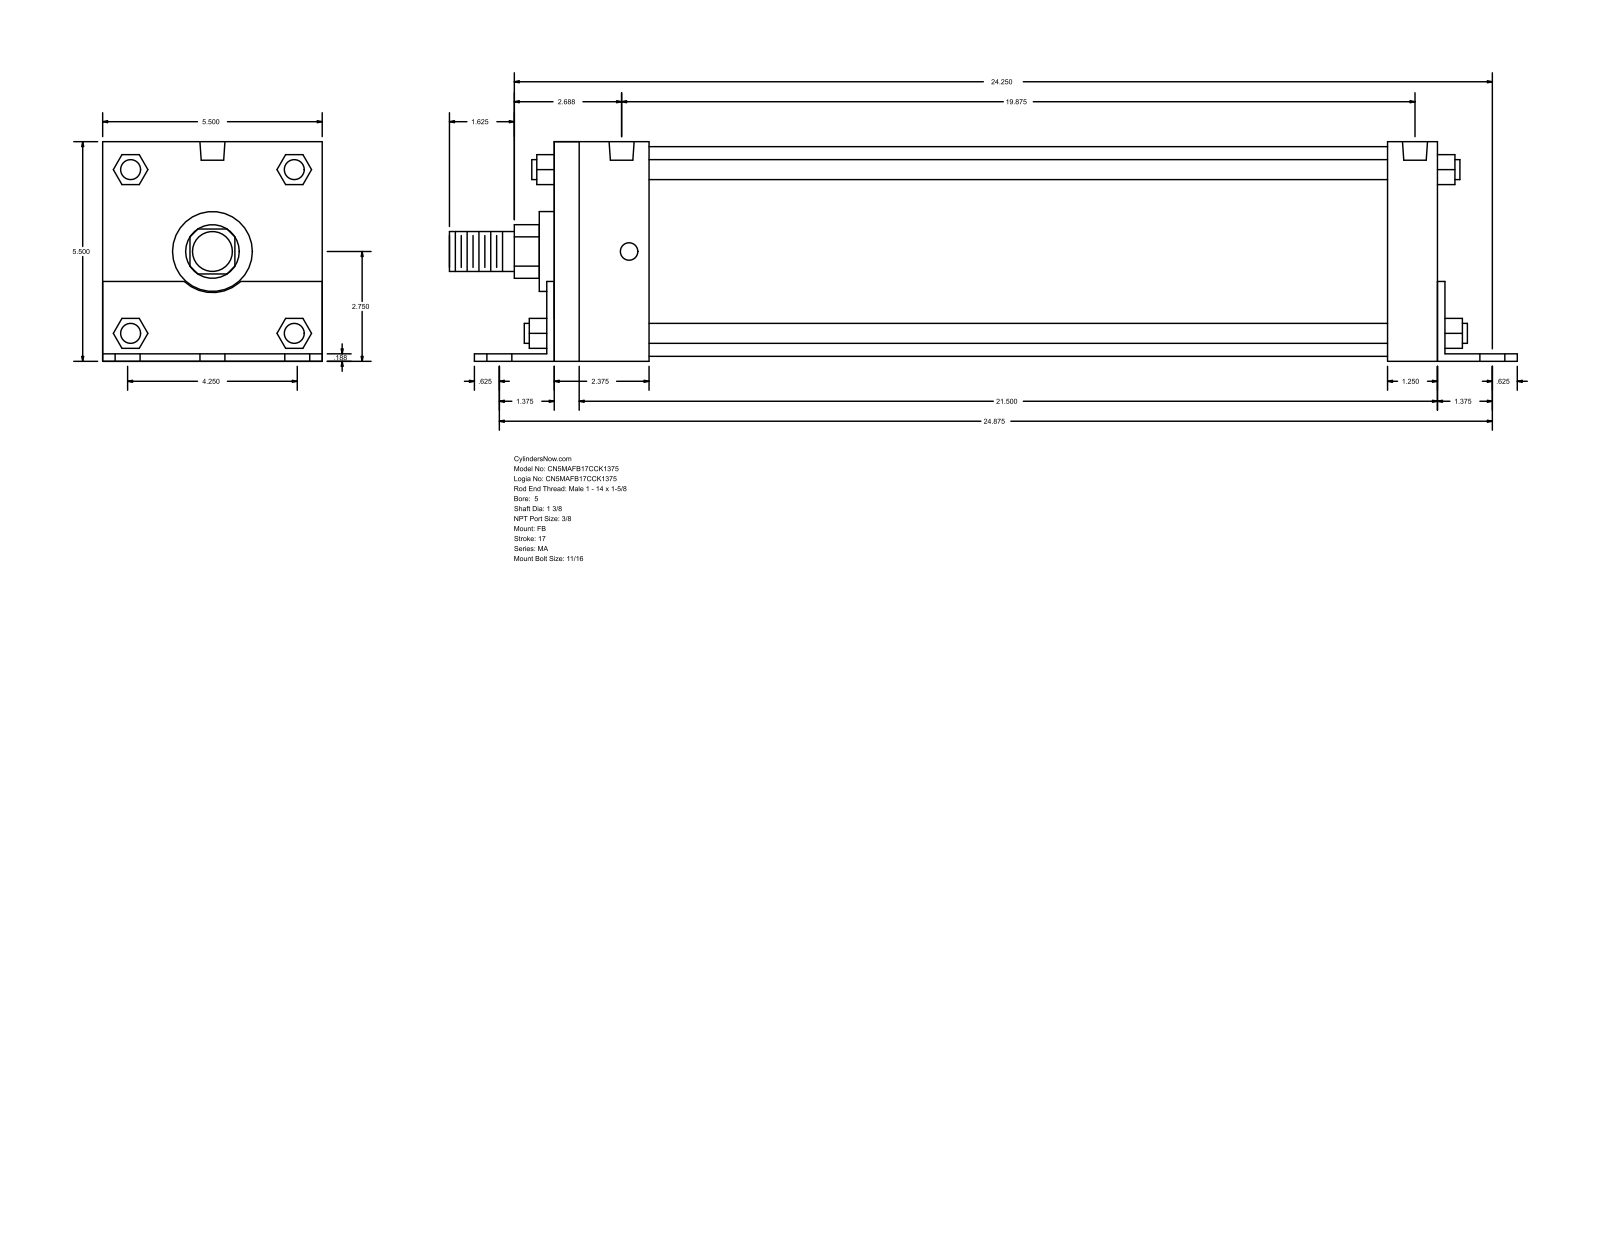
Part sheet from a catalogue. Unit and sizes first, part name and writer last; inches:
Units: inches
Overall size (bounding box): 26.75 × 5.502 × 5.5
Round holes (diameter × count): ⌀0.687 ×6, ⌀0.437 ×4, ⌀0.627 ×2
Round bosses / shafts (diameter × count): ⌀0.5 ×4, ⌀5.25 ×1, ⌀2 ×1, ⌀1.375 ×1, ⌀1 ×1
Partial cylindrical surfaces — rounded edges, fillets, slot ends (radius × count): R0.672 ×1, R1.03 ×1
Main face-to-face distances: 5.5, 0.187, 5.502, 22.313, 0.185, 5.315, 22.125, 22.5, 2.562, 2.375
Hole centre spacings: 2.125, 24.966, 24.875, 2.876, 3.005, 3.728, 3.883, 4.25
Bodies: 0 solids, 140 faces (105 planar, 35 cylindrical, 0 other)
Part name (STEP PRODUCT): MA_FB__0500_1.375
STEP written by: GSSL Pune (CONFIG_CONTROL_DESIGN)
